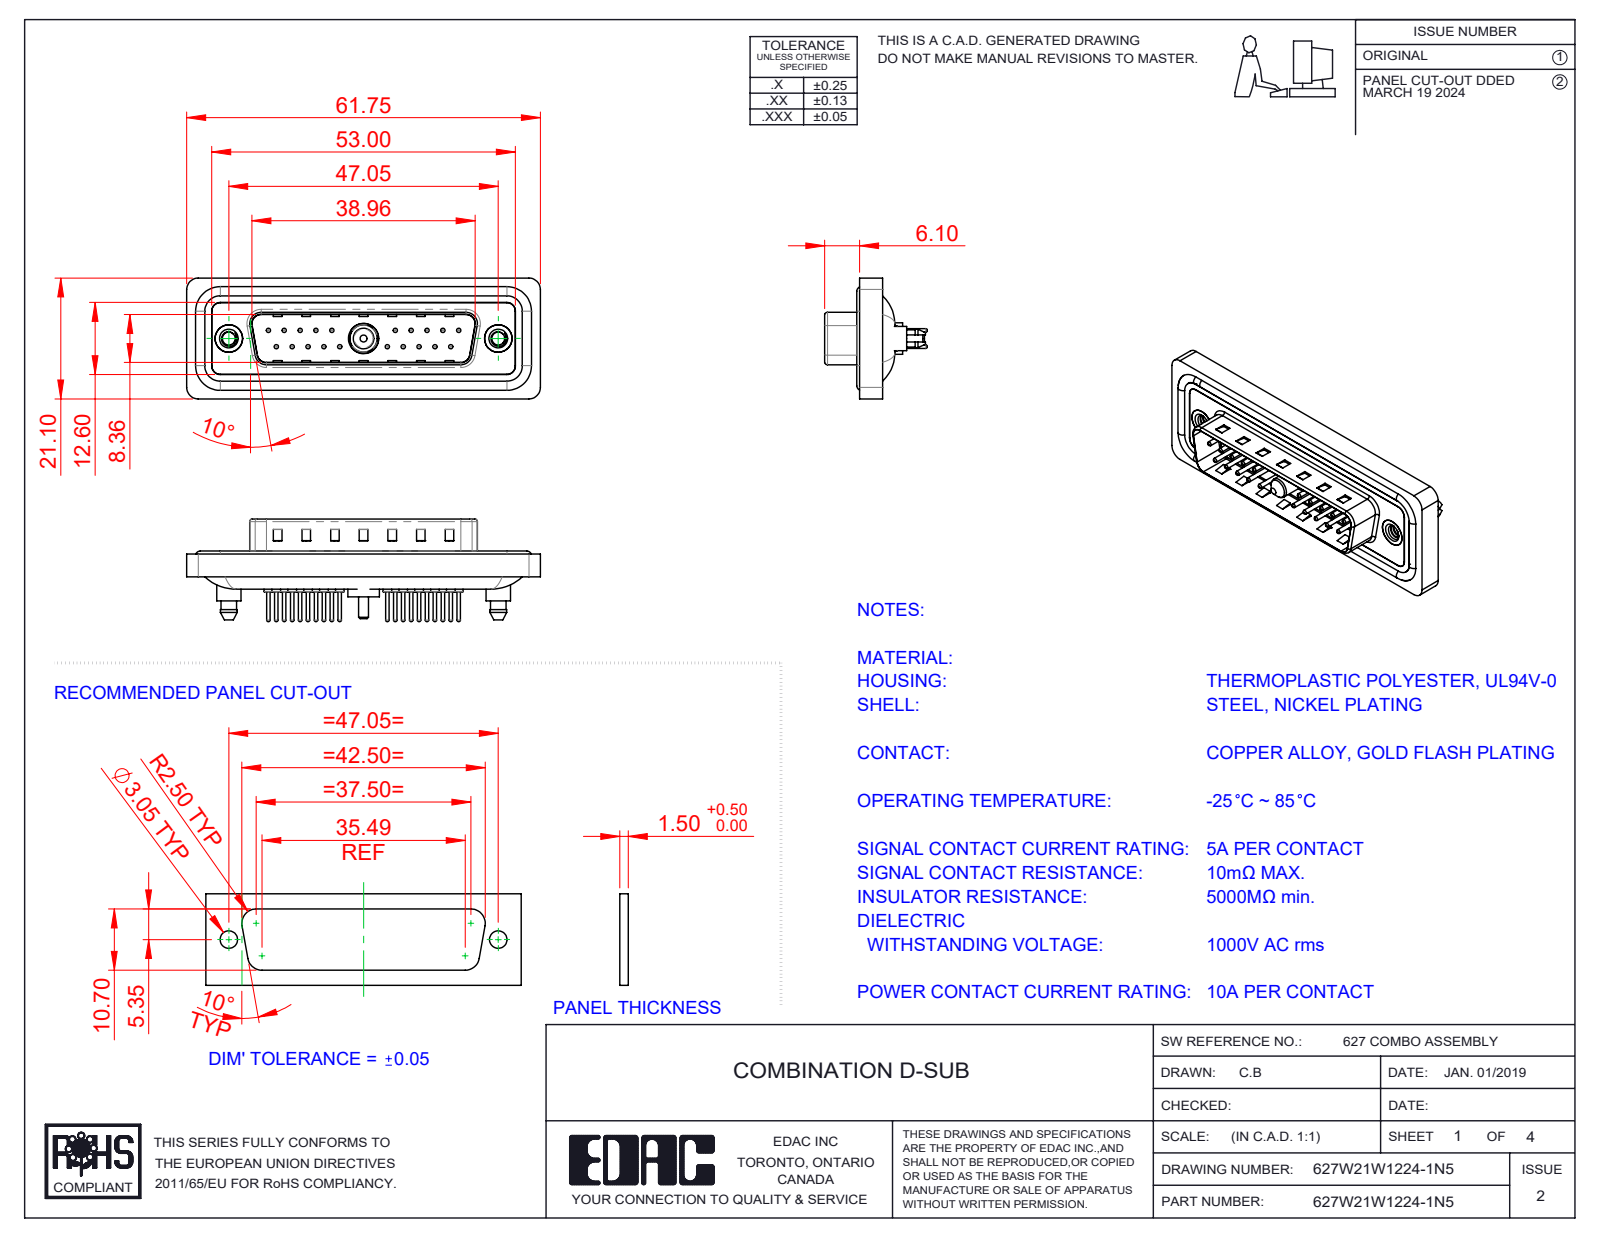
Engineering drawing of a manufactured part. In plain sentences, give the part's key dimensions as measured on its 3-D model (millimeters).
The part is named "627W21W1224-1N5; 627Combo Waterproof Housing_25 Contacts; 627Combo Contact Row 2_24; 627Combo Shell Rear_25 Contacts (+5 more)". Its 3-D file was written by "SolidWorks 2023 (CONFIG_CONTROL_DESIGN)". It is 29 solids with 1312 faces: 375 planar, 519 cylindrical and 418 other. Overall it measures 61.75 by 21.1 by 17.9 millimeters. Its volume is 7 317 cubic millimeters and its surface area 12 274 square millimeters. Round holes: 20 of diameter 0.75, 20 of diameter 1.6, 20 of diameter 2, 2 of diameter 2.26, 2 of diameter 4, 2 of diameter 4.8, 2 of diameter 5, 1 of diameter 4.85, 1 of diameter 5.3. Round bosses or shafts: 20 of diameter 1.5, 20 of diameter 0.6, 4 of diameter 1.6, 2 of diameter 5.4, 2 of diameter 4.9, 2 of diameter 4.25, 1 of diameter 5.5, 1 of diameter 5.2. Partial cylindrical surfaces (rounded edges, fillets, slot ends): 24 of radius 1.5, 18 of radius 2, 10 of radius 1.6, 8 of radius 0.5, 4 of radius 0.25, 4 of radius 0.6, 4 of radius 0.65, 4 of radius 0.9. The main face-to-face distances are 0.4, 1.5, 1.1, 1.6, 0.5, 3.1, 2.9, 4.1, 0.82, 9.58. The hole center spacings are 3.16, 2.77, 5.54, 8.31, 5.04, 19.39, 20.97, 22.16.
